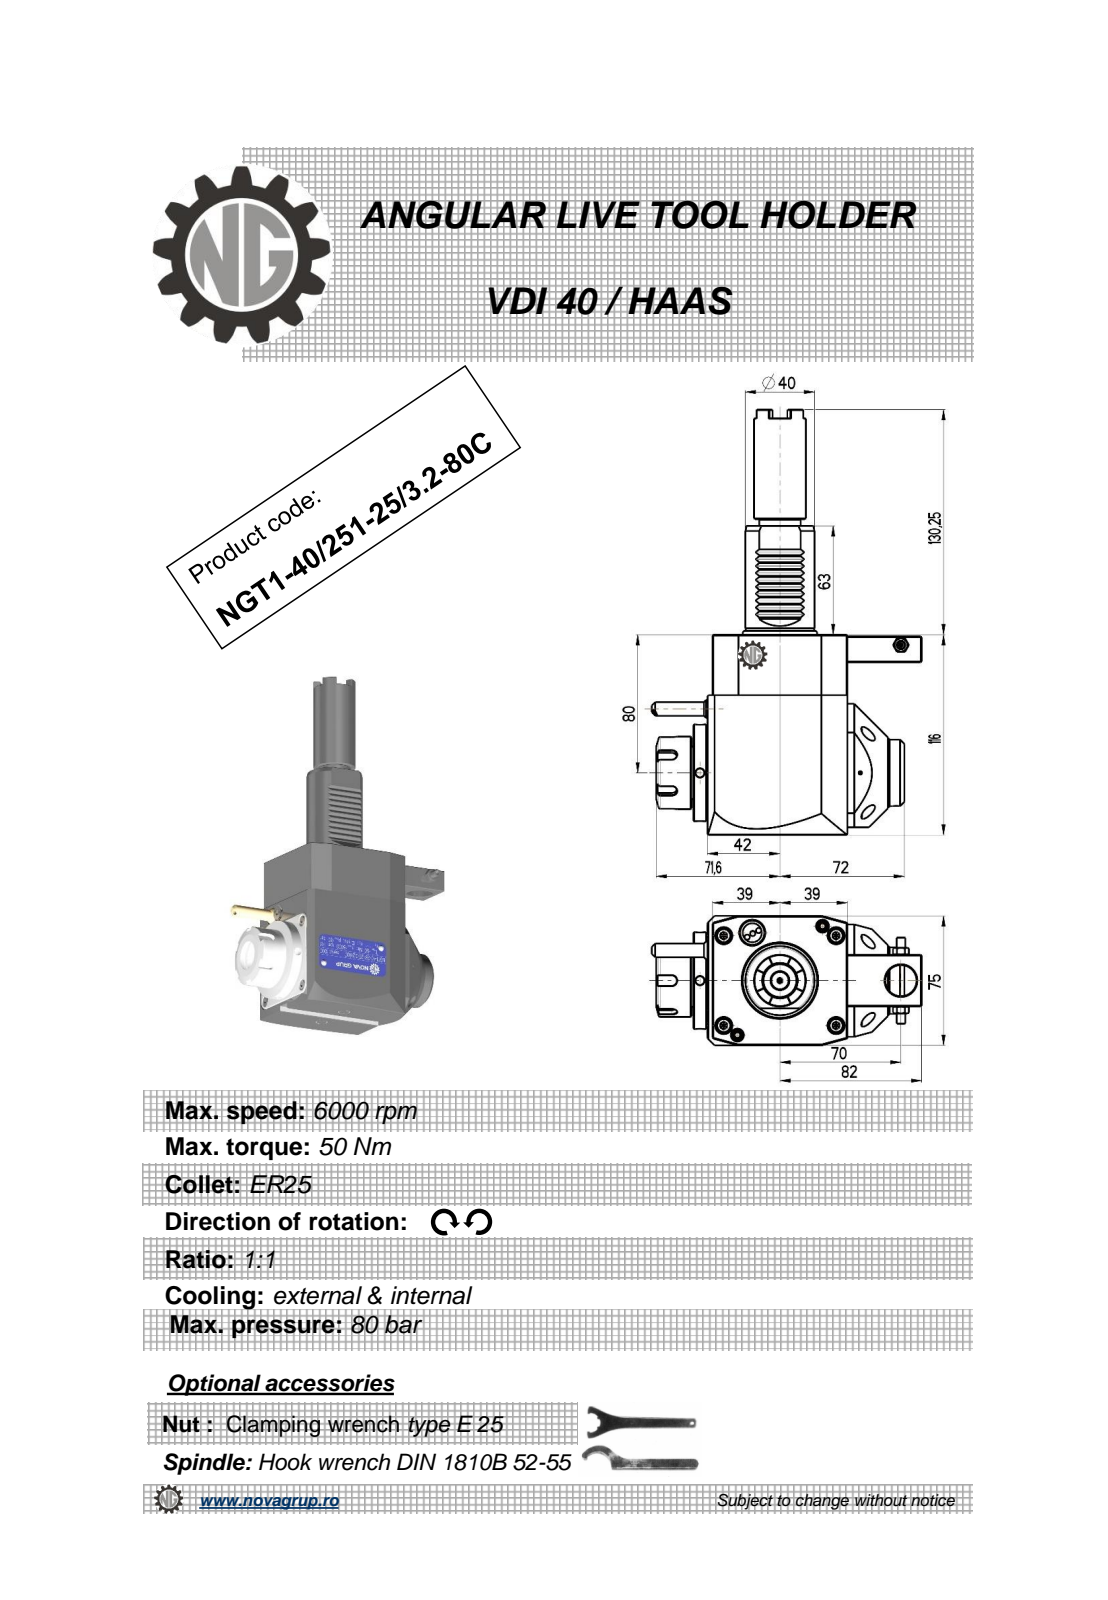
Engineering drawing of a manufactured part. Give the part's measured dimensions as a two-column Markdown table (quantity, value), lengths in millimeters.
| quantity | value |
| --- | --- |
| part name | NGT1_40_251_32_3_2_80C |
| STEP written by | PRO/ENGINEER BY PARAMETRIC TECHNOLOGY CORPORATION, 2010280 (CONFIG_CONTROL_DESIGN) |
| units | millimeters |
| bodies | 1 solid, 485 faces (224 planar, 97 cylindrical, 164 other) |
| overall size | 246.25 × 156.14 × 75 |
| volume | 939 476 mm³ |
| surface area | 82 566 mm² |
| round holes (diameter × count) | 5 × 3, 3 × 1, 4.2 × 1, 9.5 × 1, 18 × 1, 20 × 1, 20.3 × 1, 38.8 × 1, 42 × 1 |
| round bosses / shafts (diameter × count) | 56 × 1, 41.4 × 1, 40 × 1, 38.5 × 1, 38.2 × 1, 38 × 1, 36 × 1, 30 × 1 |
| partial cylindrical surfaces (radius × count) | 0.26 × 12, 0.3 × 10, 0.2 × 6, 3 × 5, 0.5 × 1, 40 × 1 |
| main face-to-face distances | 75, 116, 3, 81, 78, 111, 11, 1, 2.8, 80.8 |
| hole center spacings | 39.58, 40.93, 46.25, 70, 72.5, 116.25, 137.8 |
